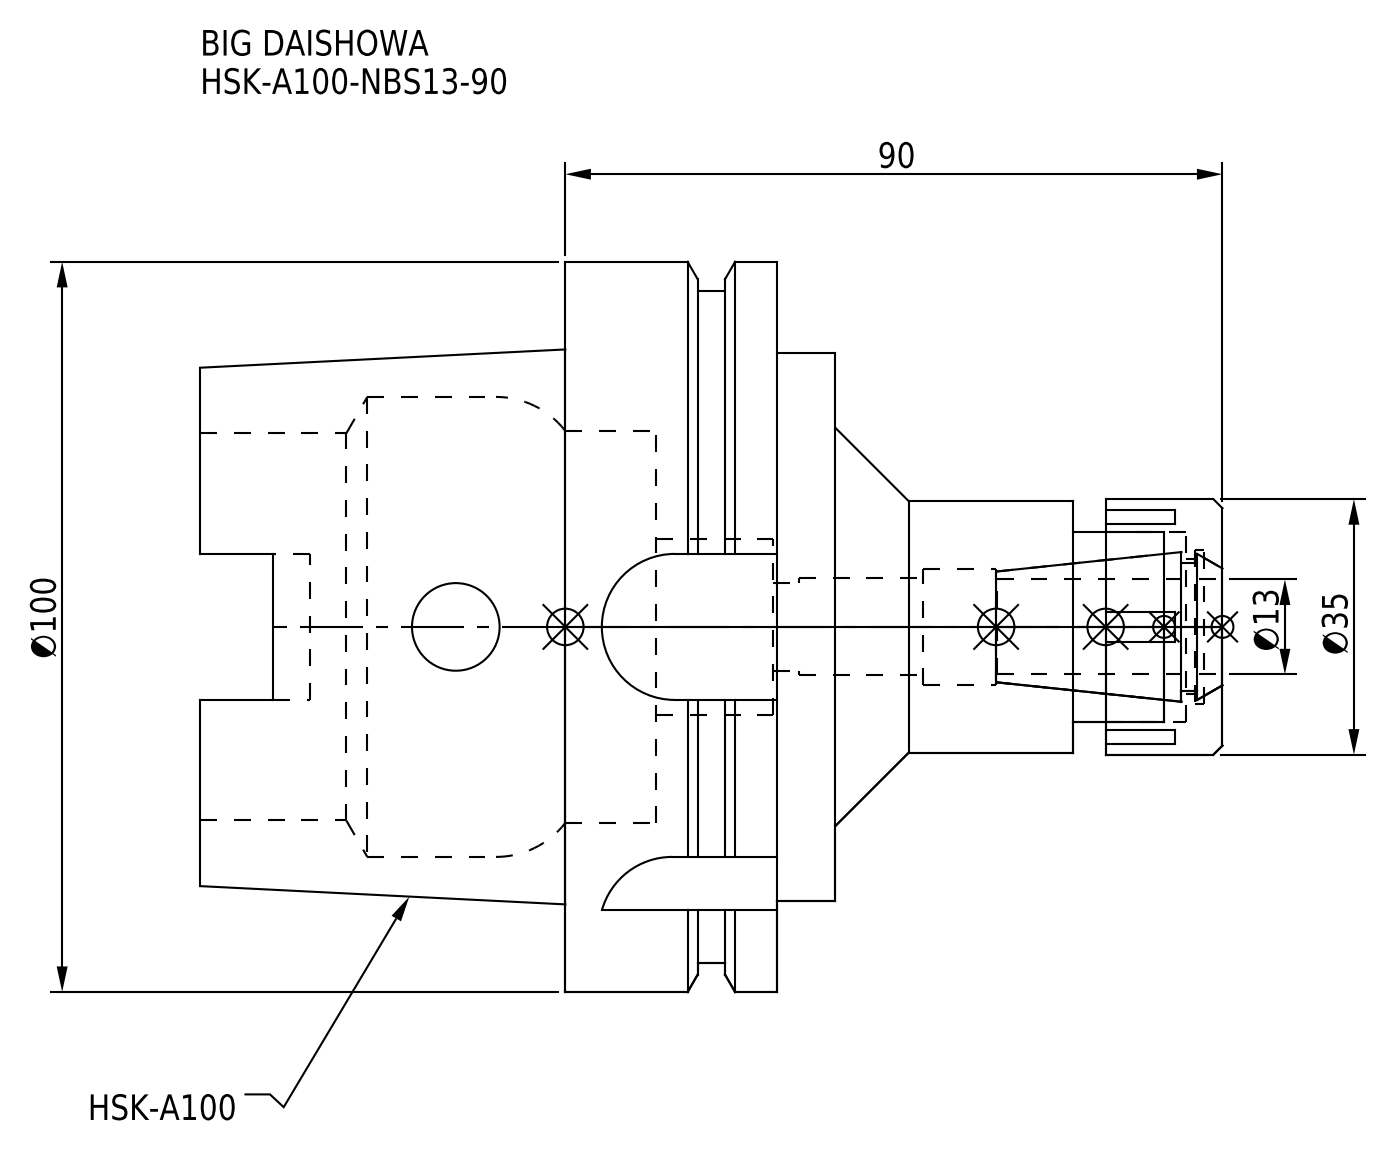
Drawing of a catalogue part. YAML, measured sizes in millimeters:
part_name: "NBN13_1.stp; HSK-A100-NBS13-90; HA100NB13090-130_ASM.stp; HSK-A100-NBS13-90-FreeParts (+3 more)"
step_written_by: "SolidWorks 2019 (CONFIG_CONTROL_DESIGN)"
units: millimeters
bodies: {solids: 2, faces: 138, planar: 66, cylindrical: 50, other: 22}
overall_size: [140, 100, 100]
volume: 329618
surface_area: 62988
round_holes:
  - {diameter: 12, count: 2}
  - {diameter: 13.3, count: 1}
  - {diameter: 16, count: 1}
  - {diameter: 18.5, count: 1}
  - {diameter: 21, count: 1}
  - {diameter: 24, count: 1}
  - {diameter: 26, count: 1}
  - {diameter: 53, count: 1}
  - {diameter: 53.8, count: 1}
  - {diameter: 63, count: 1}
round_bosses_or_shafts:
  - {diameter: 100, count: 1}
  - {diameter: 92, count: 1}
  - {diameter: 75, count: 1}
  - {diameter: 35, count: 1}
  - {diameter: 34.5, count: 1}
partial_cylinders:
  - {radius: 4.88, count: 4}
  - {radius: 10, count: 4}
face_to_face_distances: [29, 8, 37, 24.55, 16.55, 12.45, 50, 87, 79, 62.45]
